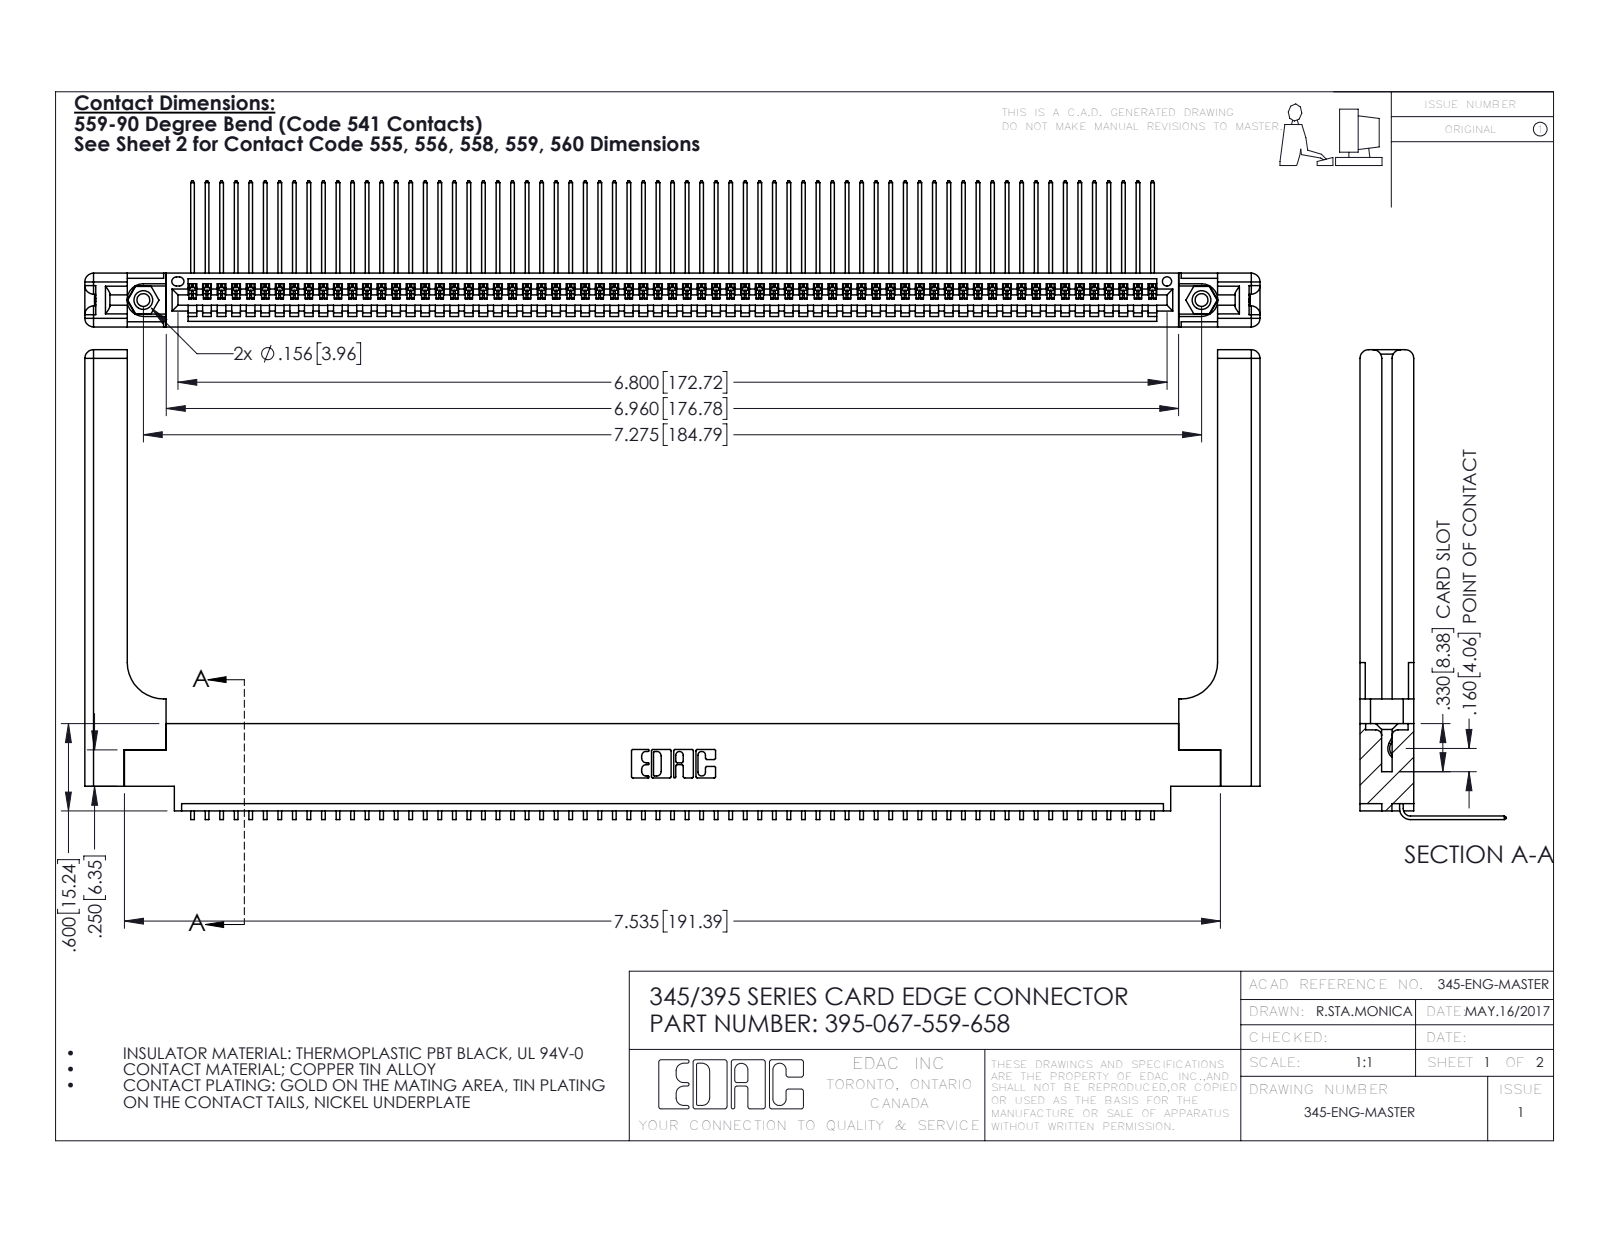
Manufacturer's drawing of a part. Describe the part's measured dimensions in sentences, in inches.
The part is named "345-220-058_345-220-058; 345-250-001_345-250-001-102; 395-067-559-658; 345-292-001_558 559 Tail - 1 (+1 more)". Its 3-D file was written by "SolidWorks 2016 (CONFIG_CONTROL_DESIGN)". It is 72 solids with 4406 faces: 3046 planar, 1300 cylindrical and 60 other. Overall it measures 8.079 by 3.229 by 1.005 inches. Its volume is 1.728 cubic inches and its surface area 51.77 square inches. Round holes: 2 of diameter 0.089, 2 of diameter 0.125, 2 of diameter 0.156, 1 of diameter 0.064. Round bosses or shafts: 2 of diameter 0.155. Partial cylindrical surfaces (rounded edges, fillets, slot ends): 134 of radius 0.006, 22 of radius 0.01, 16 of radius 0.06, 6 of radius 0.007, 6 of radius 0.031, 3 of radius 0.026, 2 of radius 0.03, 2 of radius 0.031. The main face-to-face distances are 0.072, 0.37, 0.298, 0.098, 0.272, 0.025, 0.2, 0.225, 0.148, 0.15. The hole center spacings are 0.27, 7.039, 7.275.
